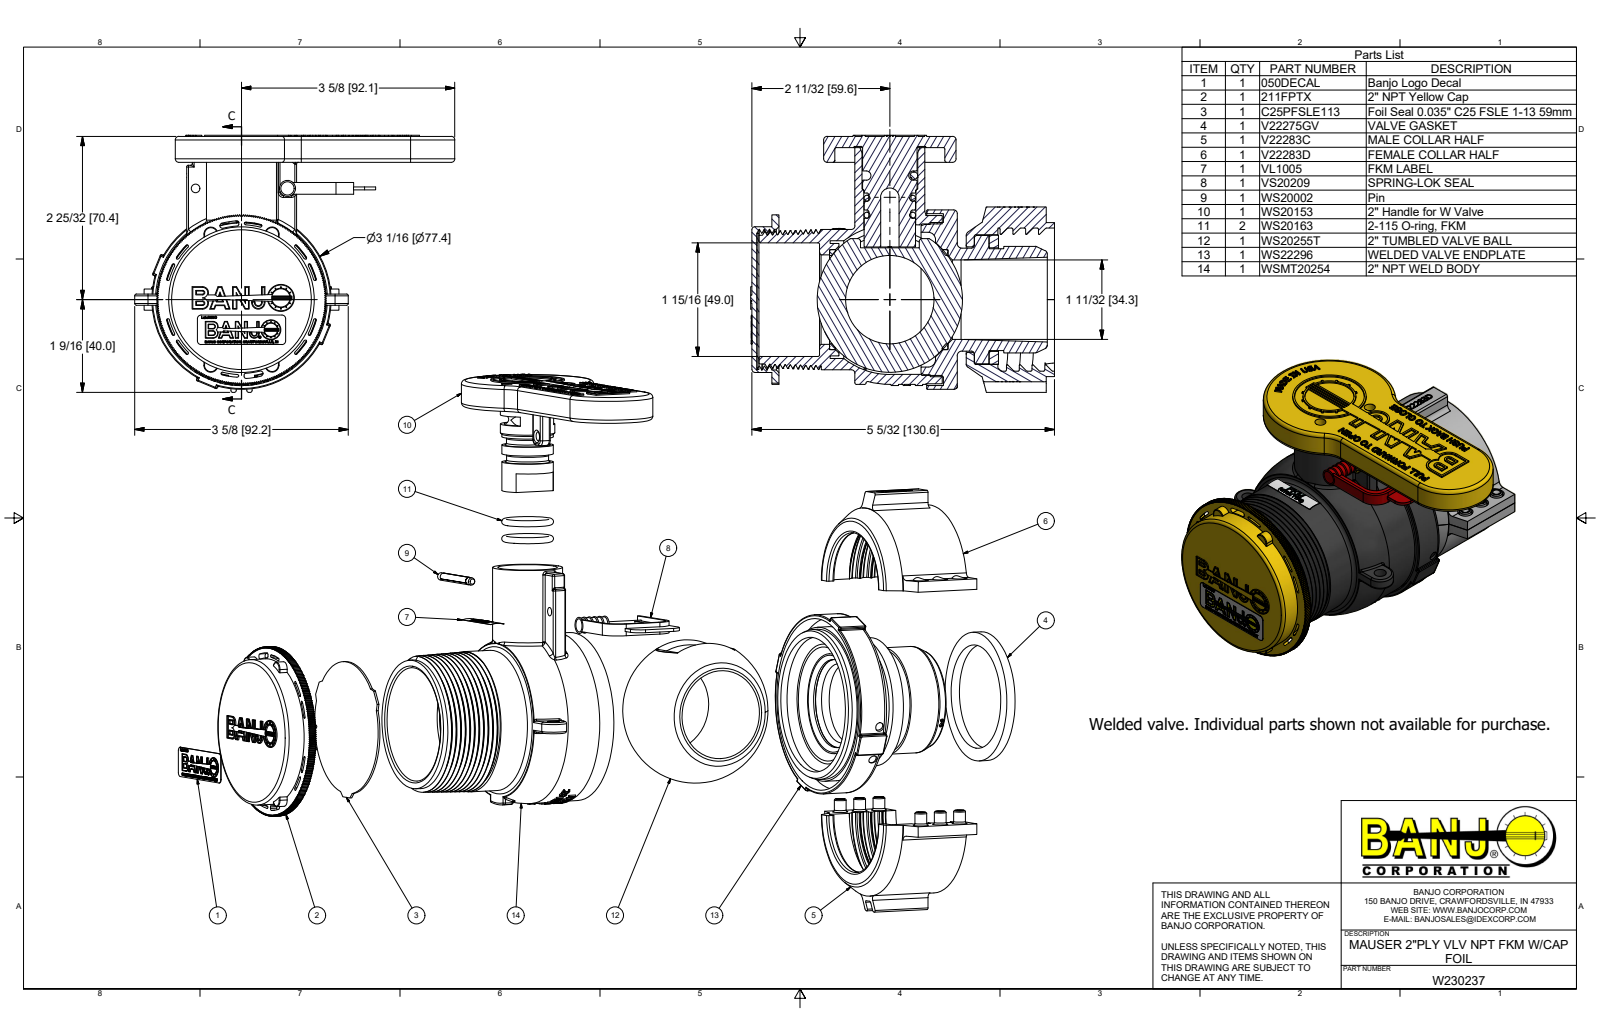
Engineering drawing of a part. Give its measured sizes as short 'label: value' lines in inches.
name: W230237; WSMT20254; WSMT20254X; 050DECAL (+8 more)
written by: Autodesk Inventor 2018 (AUTOMOTIVE_DESIGN)
unit: in
bodies: 17 solids, 4819 faces (2541 planar, 993 cylindrical, 1285 other)
size: 40.178 × 5.44 × 4.368
volume: 19.42 in³; area: 507.9 in²
holes: 6× ⌀0.209, 6× ⌀0.257, 2× ⌀0.145, 2× ⌀0.15, 2× ⌀0.188, 2× ⌀0.207, 2× ⌀1.5, 1× ⌀0.156, 1× ⌀0.227, 1× ⌀0.309, 1× ⌀0.312, 1× ⌀0.321
bosses: 6× ⌀0.2, 2× ⌀2.25, 1× ⌀3.047, 1× ⌀2.92, 1× ⌀2.88, 1× ⌀2.858, 1× ⌀2.62, 1× ⌀2.615
rounds: 76× R0.03, 24× R0.015, 10× R0.09, 4× R0.06, 4× R0.062, 4× R0.118, 4× R0.25, 3× R0.01
face distances: 0.085, 0.12, 0.035, 0.19, 3.371, 3.406, 3.491, 0.25, 0.02, 0.54
hole spacings: 2.881, 2.857, 0.375, 0.375, 0.75, 1.633, 2.045, 2.214
